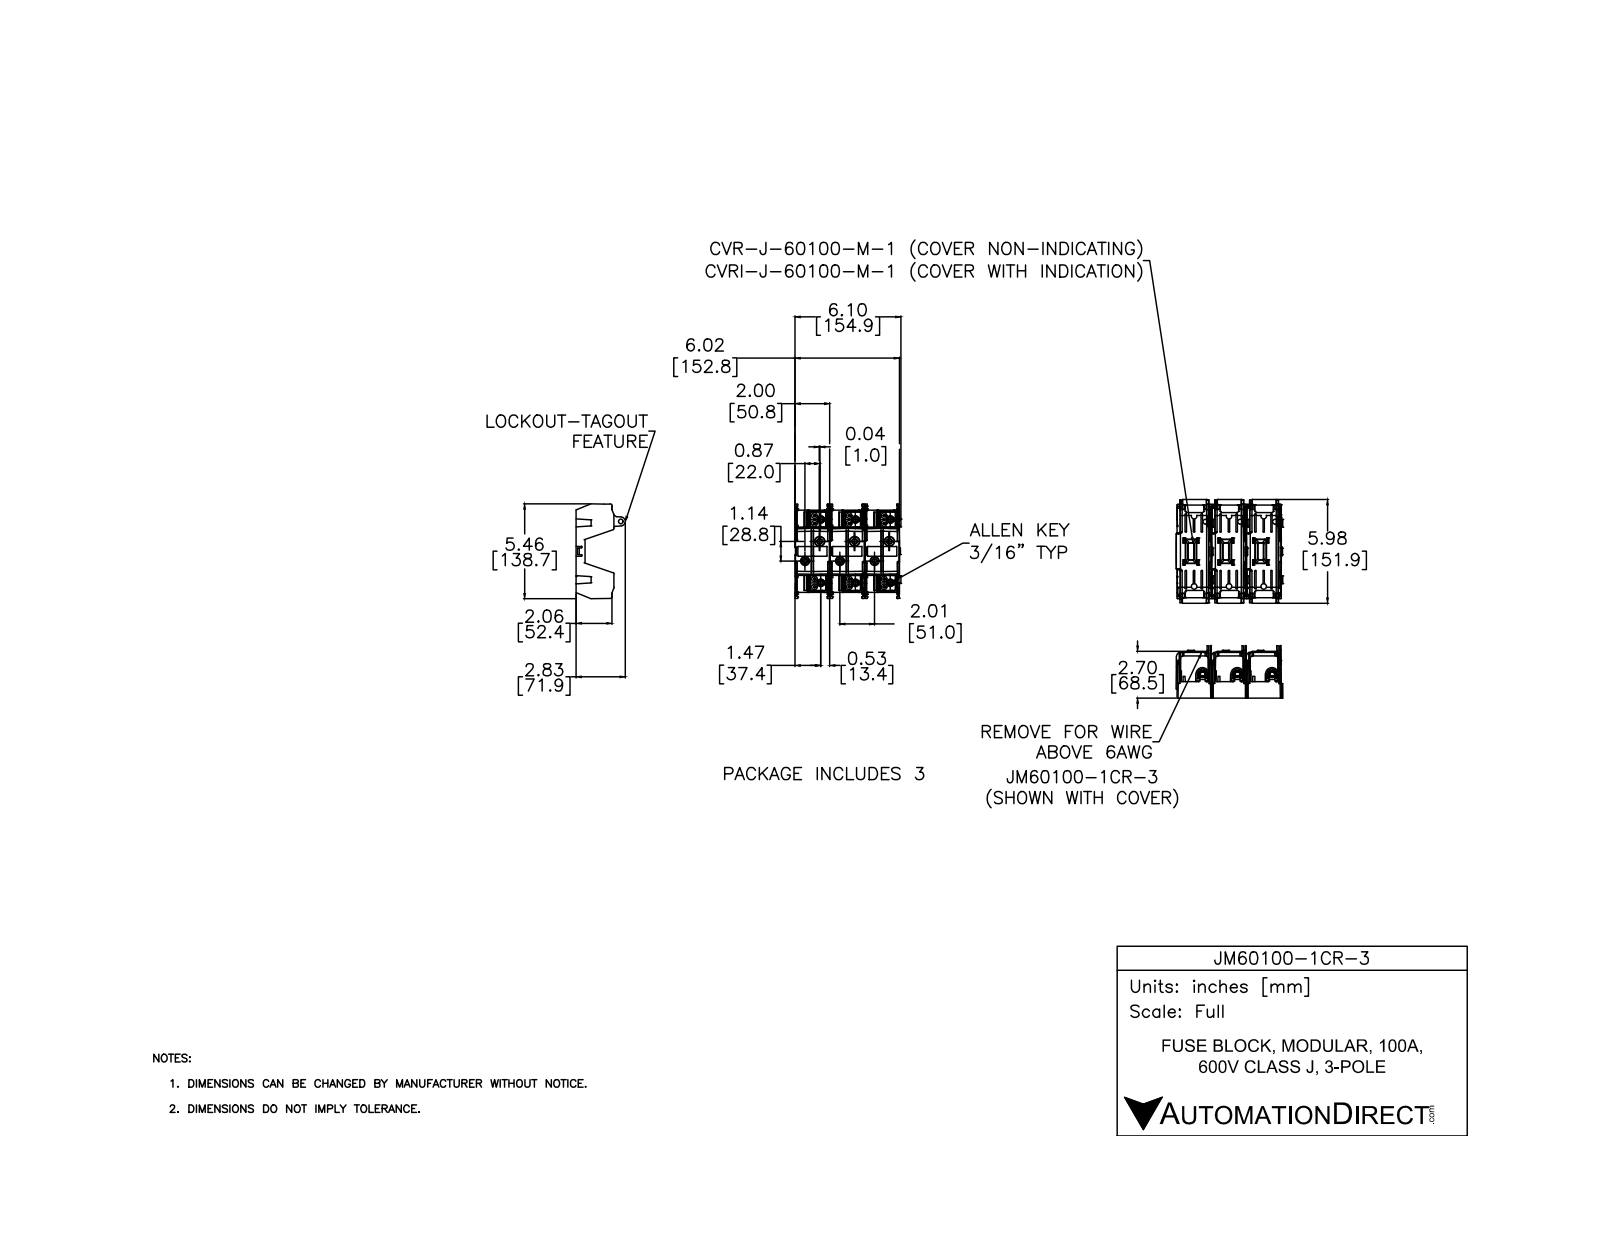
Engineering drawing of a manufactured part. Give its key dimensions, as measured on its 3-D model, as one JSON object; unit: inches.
{"part_name": "JM60100-1CR-3", "step_written_by": "SolidWorks 2021 (CONFIG_CONTROL_DESIGN)", "units": "inches", "bodies": {"solids": 0, "faces": 2643, "planar": 843, "cylindrical": 1155, "other": 645}, "overall_size": [6.113, 5.463, 2.829], "round_holes": [[0.19, 6], [0.25, 6]], "round_bosses_or_shafts": [[0.306, 12], [0.039, 12], [0.437, 6], [0.437, 6], [0.406, 3], [0.236, 2], [0.277, 1]], "partial_cylinders_radius": [[0.02, 207], [0.01, 132], [0.015, 96], [0.02, 70], [0.01, 69], [0.03, 24], [0.079, 20], [0.158, 14]], "face_to_face_distances": [2.01, 1.898, 2.01, 4.02, 4.02, 3.908, 0.112, 0.95, 0.247, 0.025], "hole_center_spacings": [3.674, 3.675, 3.713, 0.07, 0.07, 0.141, 0.535, 0.535]}
